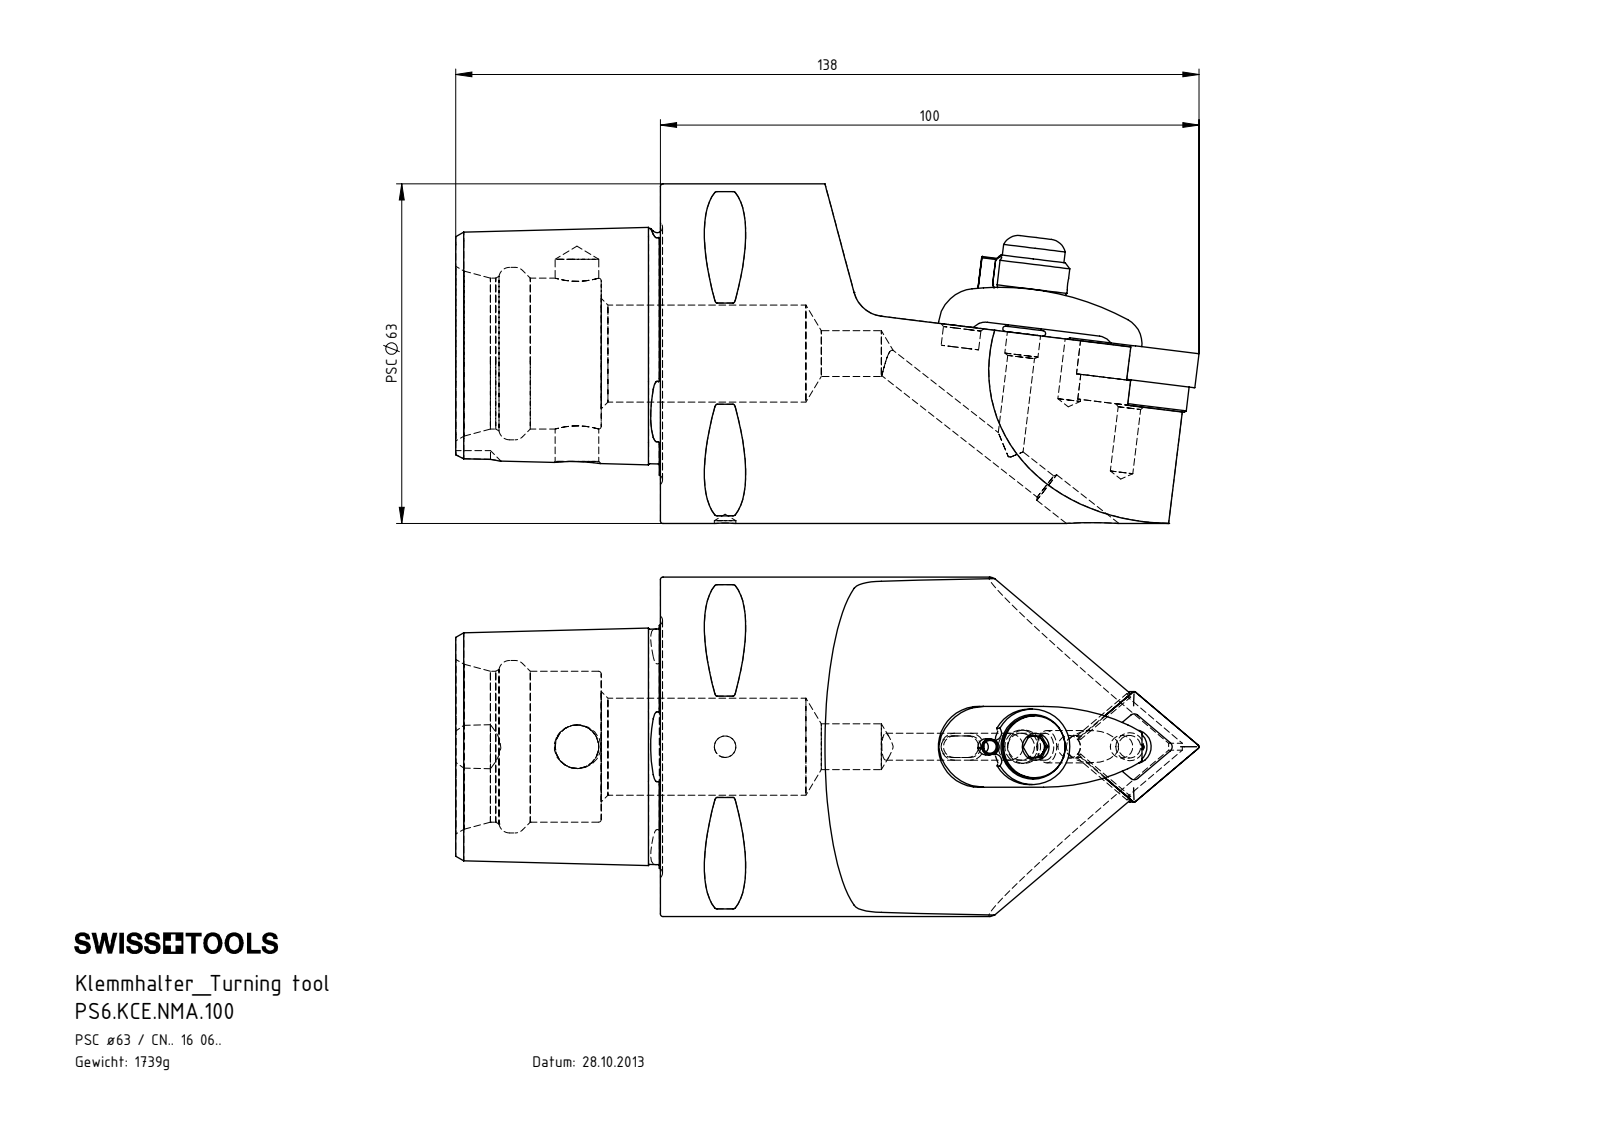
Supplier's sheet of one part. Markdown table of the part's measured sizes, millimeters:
| quantity | value |
| --- | --- |
| part name | PS6-KCE.NMA.100; ISO 13337 - 3 x 12_PreviewCfg; WCC-ER5.102.012_B; WCC-ER5.102.005_A (+7 more) |
| STEP written by | SolidWorks 2012 (CONFIG_CONTROL_DESIGN) |
| units | millimeters |
| bodies | 11 solids, 418 faces (97 planar, 128 cylindrical, 193 other) |
| overall size | 138 × 63 × 63 |
| volume | 220 385 mm³ |
| surface area | 38 191 mm² |
| round holes (diameter × count) | 2 × 3, 5 × 3, 4.2 × 2, 7 × 2, 8.5 × 2, 2.4 × 1, 3 × 1, 4 × 1, 6 × 1, 6.2 × 1, 6.35 × 1, 8.05 × 1 |
| round bosses / shafts (diameter × count) | 6 × 2, 3 × 2, 63 × 1, 14 × 1, 11.5 × 1, 6.8 × 1, 6.2 × 1, 5 × 1 |
| partial cylindrical surfaces (radius × count) | 0.5 × 8, 1.5 × 7, 0.45 × 6, 0.4 × 4, 0.79 × 4, 0.79 × 2, 2 × 2, 3 × 2 |
| main face-to-face distances | 38, 6.06, 15.06, 24.88, 4.77, 10.83, 12.12, 7.35, 1.29, 27 |
| hole center spacings | 7.99, 8, 9.8, 20.6, 28.6, 29.1, 0.5, 8.19 |
